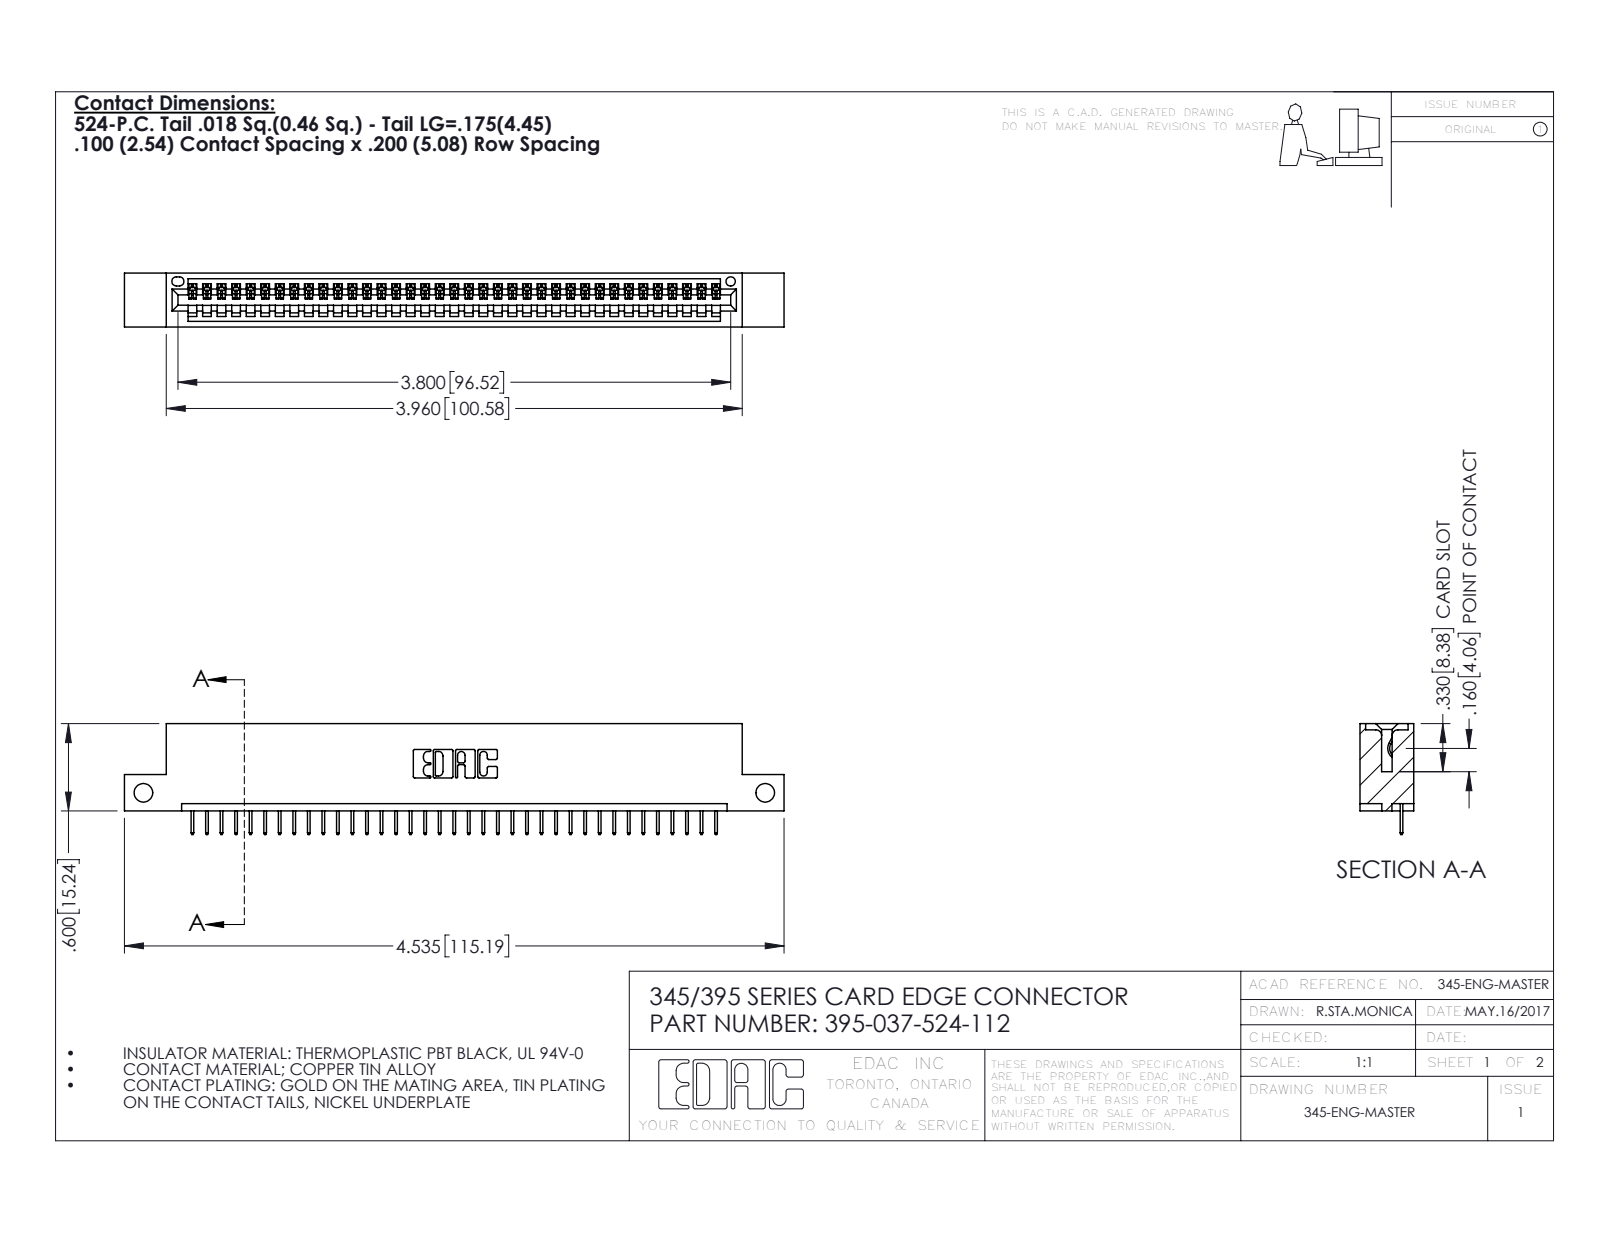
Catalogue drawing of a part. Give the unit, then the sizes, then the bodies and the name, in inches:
Units: inches
Overall size (bounding box): 4.535 × 0.762 × 0.37
Round holes (diameter × count): ⌀0.128 ×2, ⌀0.064 ×1
Partial cylindrical surfaces — rounded edges, fillets, slot ends (radius × count): R0.006 ×74, R0.01 ×22, R0.007 ×6, R0.031 ×6, R0.026 ×3, R0.031 ×2, R0.04 ×2, R0.014 ×1
Main face-to-face distances: 0.072, 0.298, 0.37, 0.2, 0.098, 0.272, 0.025, 0.225, 0.072, 0.149
Hole centre spacings: 4.275
Volume: 0.651 in³ · Surface area: 20.92 in²
Bodies: 38 solids, 2420 faces (1782 planar, 638 cylindrical, 0 other)
Part name (STEP PRODUCT): 345-292-001_345-293-124; 345 Part_Flush Mounting Lugs - Side Mount; 395-037-524-112
STEP written by: SolidWorks 2016 (CONFIG_CONTROL_DESIGN)
